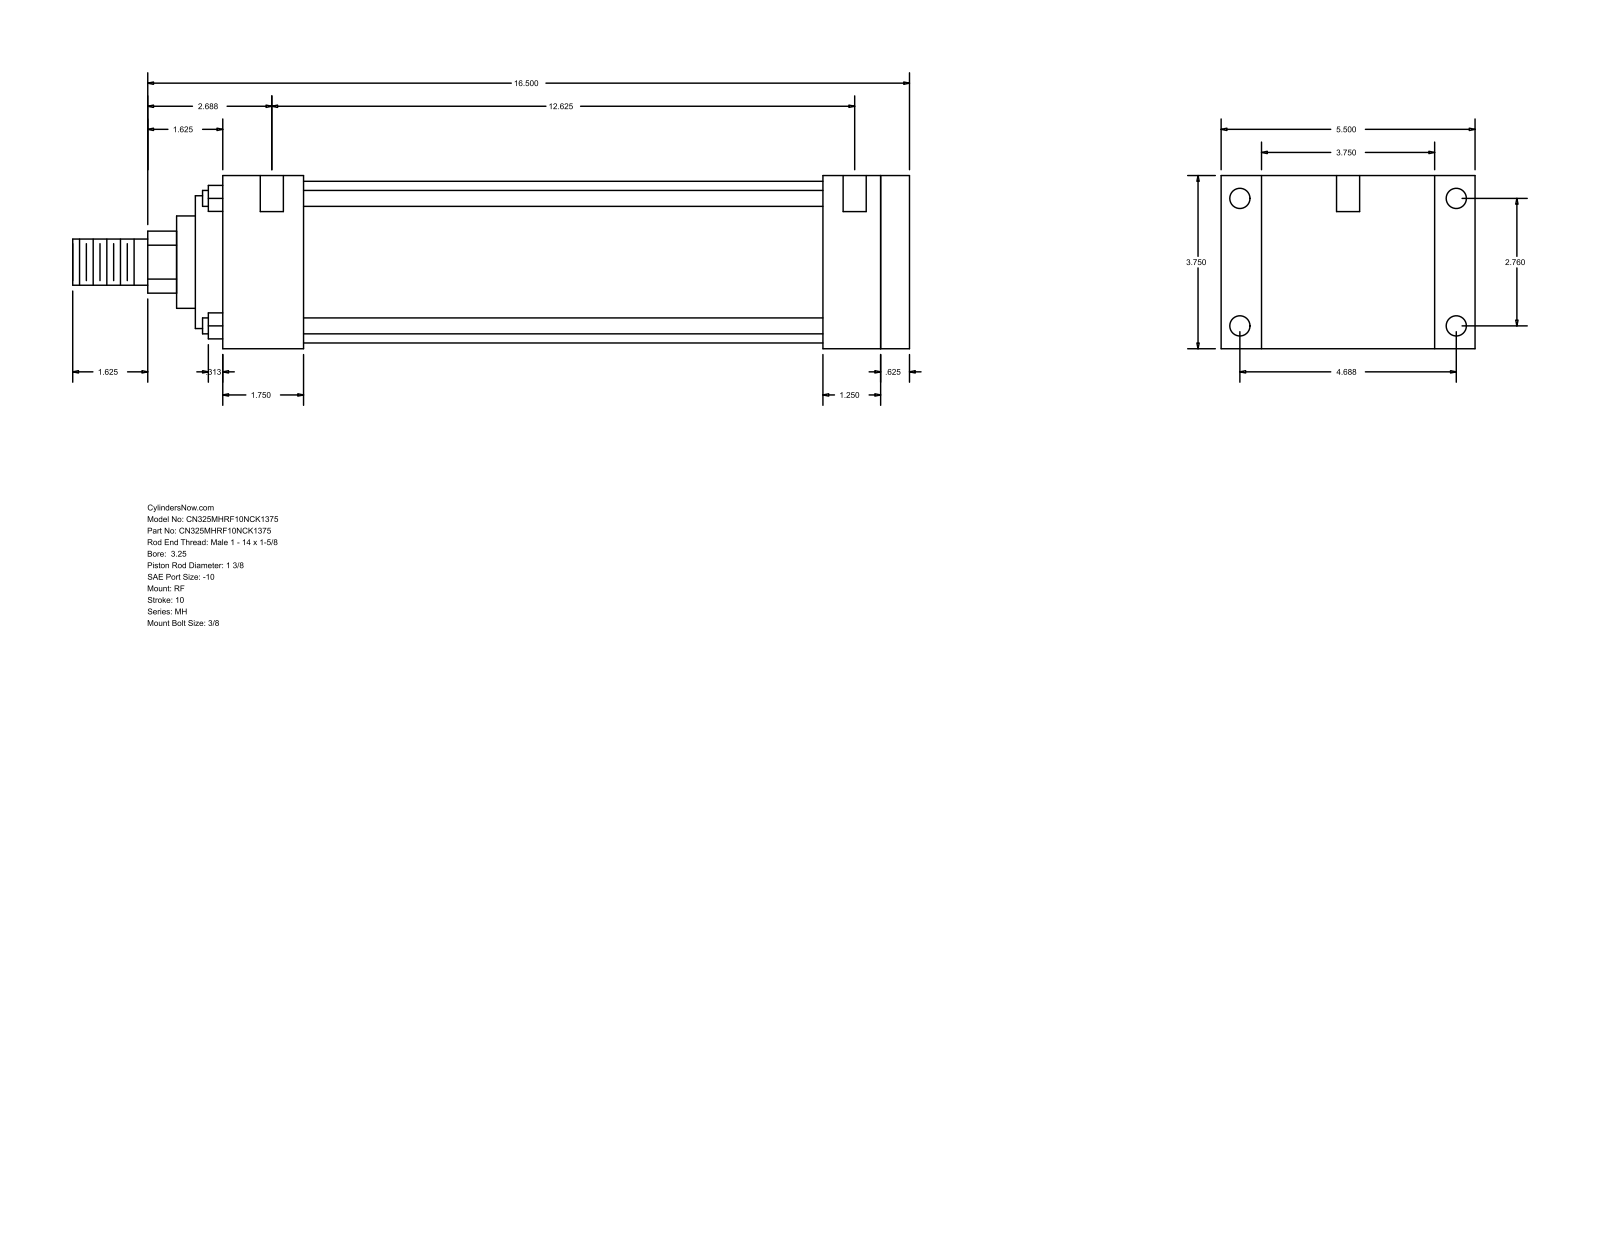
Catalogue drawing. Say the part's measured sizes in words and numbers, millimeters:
The part is named "MH_RF__0325_1.375". Its 3-D file was written by "GSSL Pune (CONFIG_CONTROL_DESIGN)". It is 0 solids with 94 faces: 65 planar, 29 cylindrical and 0 other. Overall it measures 460.38 by 139.7 by 95.25 millimeters. Round holes: 4 of diameter 5.56, 4 of diameter 11.13, 2 of diameter 12.7. Round bosses or shafts: 4 of diameter 8.76, 1 of diameter 88.9, 1 of diameter 73.03, 1 of diameter 50.8, 1 of diameter 34.92, 1 of diameter 25.4. Partial cylindrical surfaces (rounded edges, fillets, slot ends): 1 of radius 17.06. The main face-to-face distances are 95.24, 377.83, 361.96, 15.87, 22.23, 117.47, 44.45, 317.51, 333.38, 330.21. The hole center spacings are 70.1, 119.06, 138.16, 327.03, 1.59, 4.76, 320.68, 322.27.
